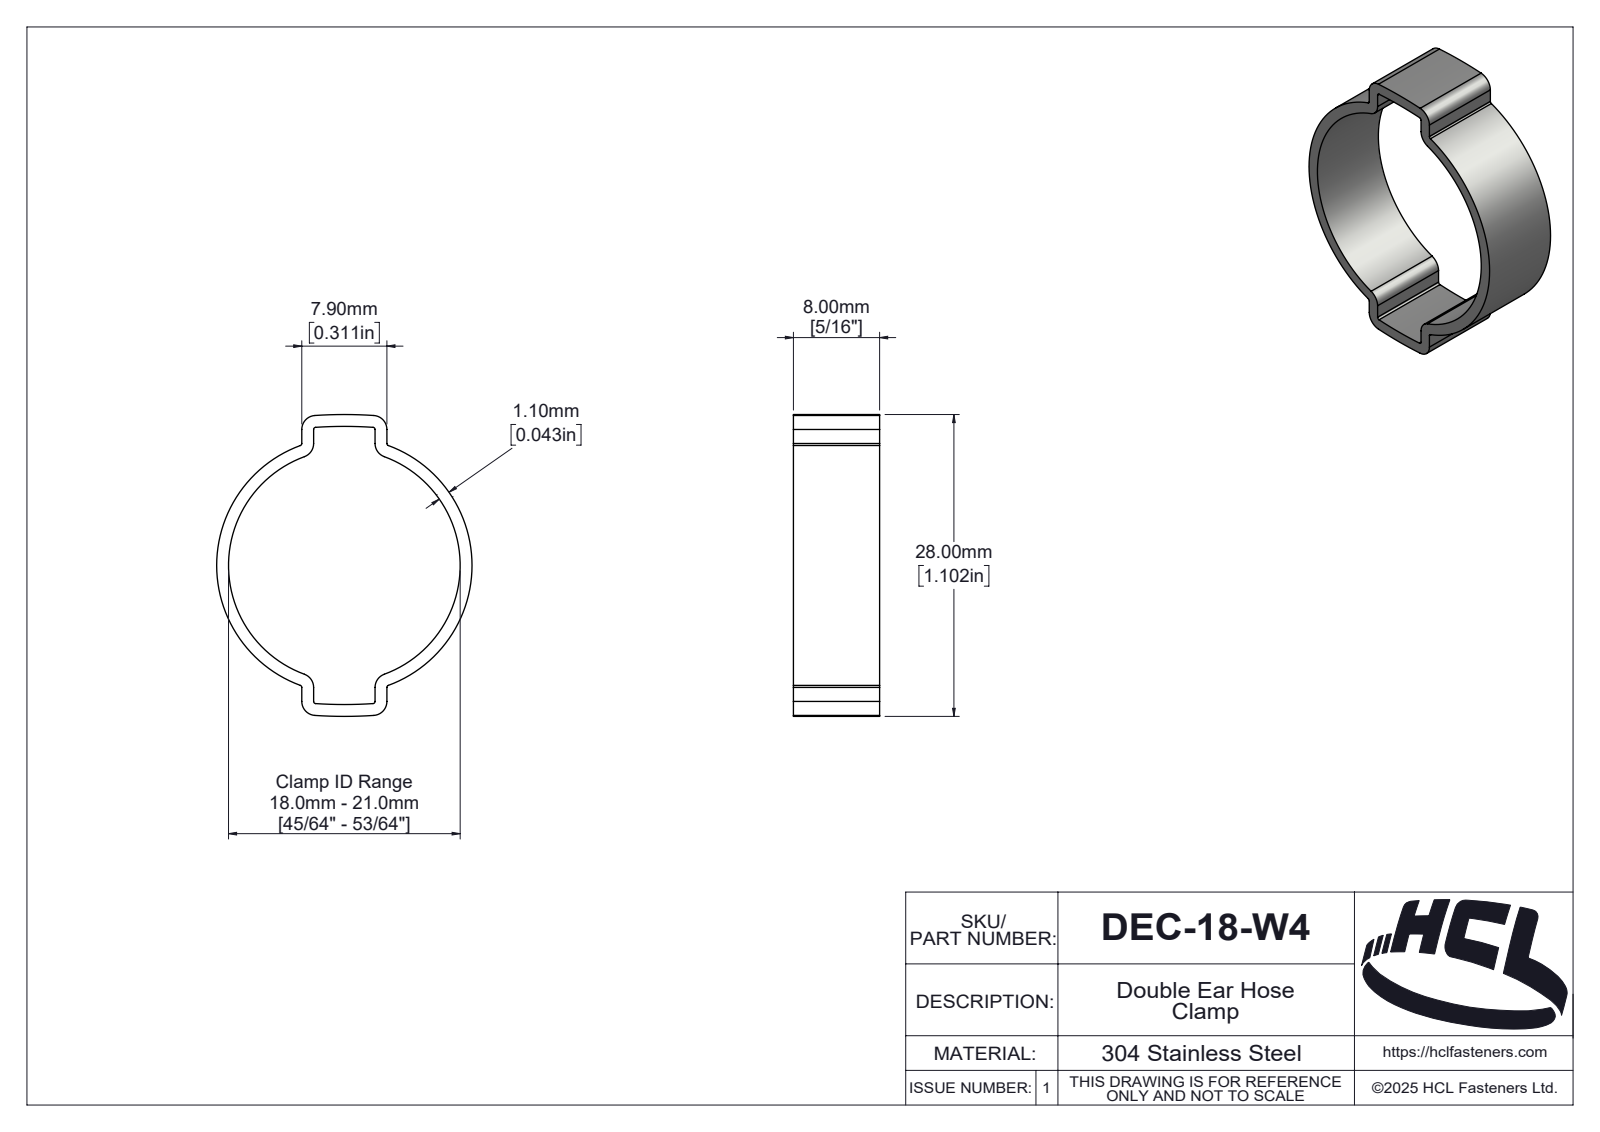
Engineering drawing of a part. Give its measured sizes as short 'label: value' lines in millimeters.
name: DEC-18-W4
written by: SolidWorks 2025 (AUTOMOTIVE_DESIGN)
unit: mm
bodies: 1 solid, 137 faces (12 planar, 67 cylindrical, 58 other)
size: 28 × 23.7 × 8
volume: 697 mm³; area: 1 447 mm²
rounds: 8× R0.2, 8× R1.3, 2× R40.66, 2× R41.76, 1× R0.2, 1× R0.81, 1× R1.01, 1× R1.06
face distances: 8, 1.1, 6.8, 7.9, 5.7, 3.83, 2.73, 2.97, 4.07, 3.68
